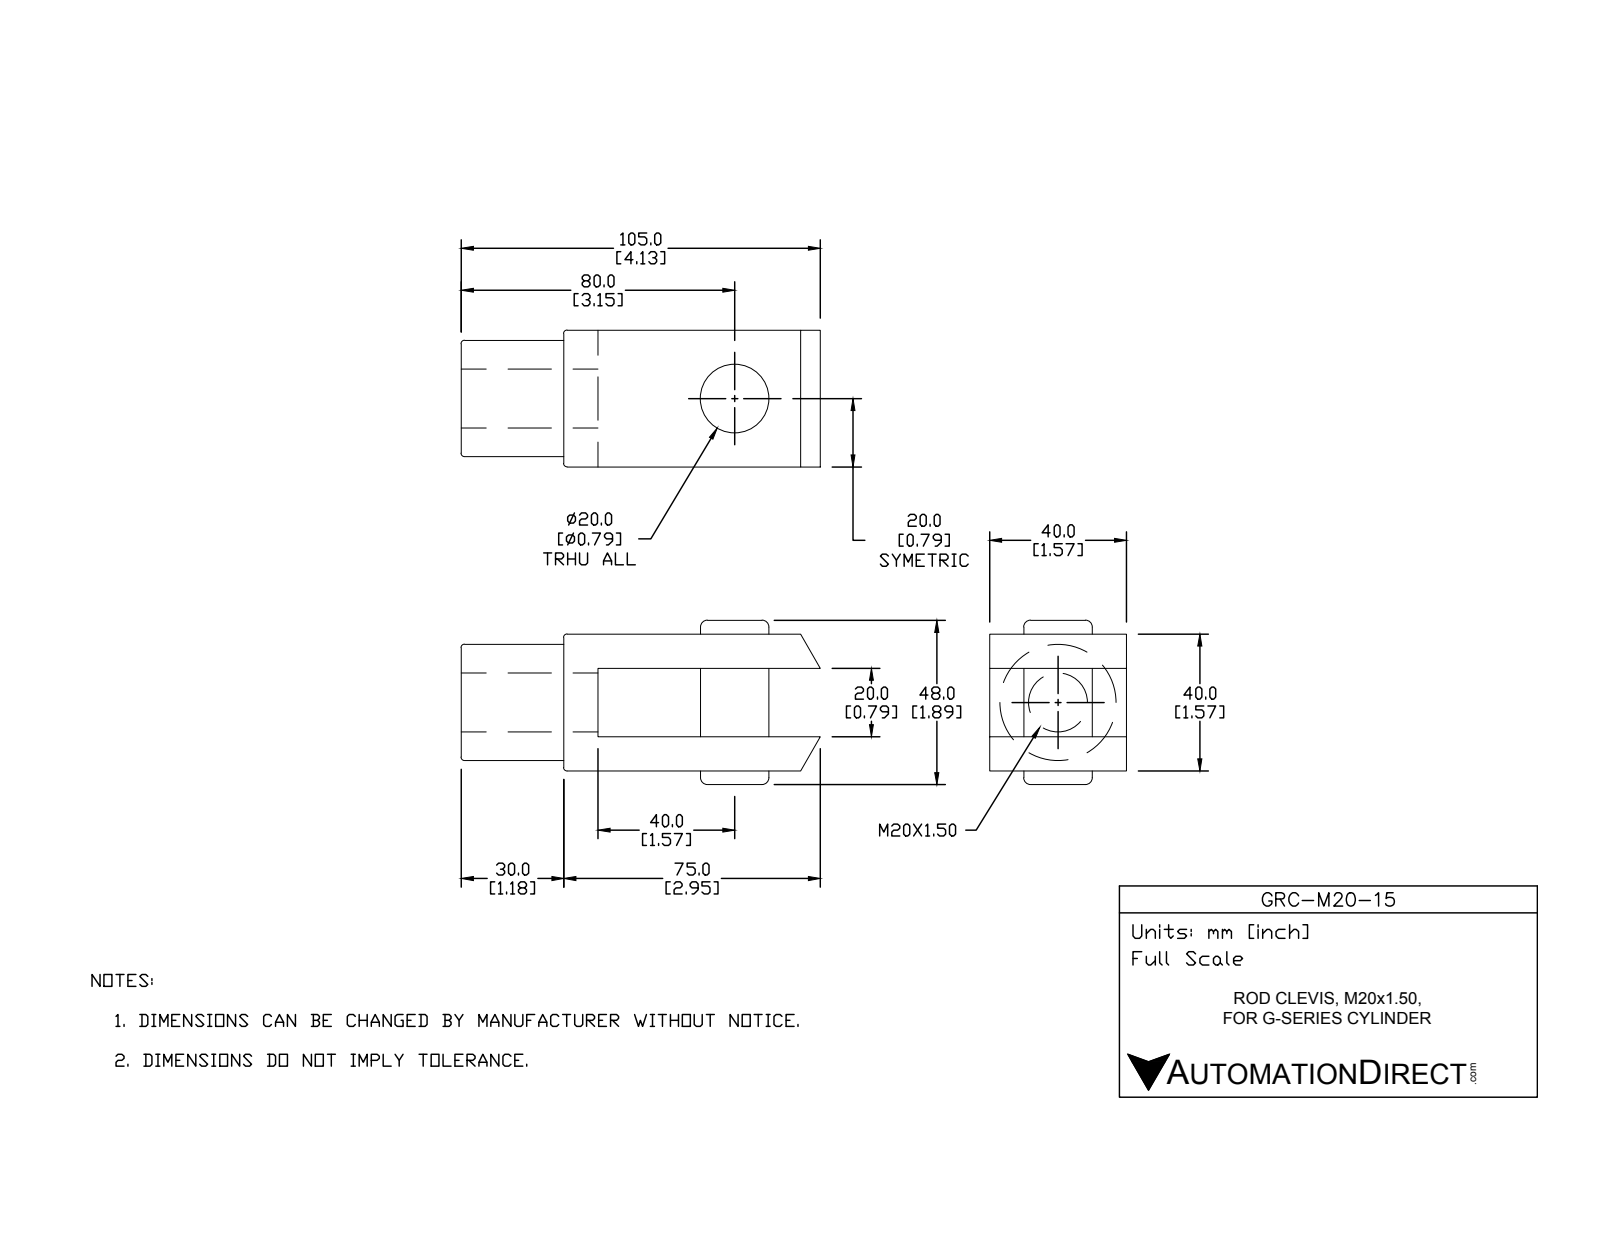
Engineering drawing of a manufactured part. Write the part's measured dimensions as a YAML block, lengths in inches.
part_name: "GRC-M20-15"
step_written_by: "SolidWorks 2017 (AUTOMOTIVE_DESIGN)"
units: inches
bodies: {solids: 1, faces: 33, planar: 13, cylindrical: 14, other: 6}
overall_size: [4.134, 1.89, 1.575]
volume: 5.444
surface_area: 35.81
round_holes:
  - {diameter: 0.728, count: 1}
round_bosses_or_shafts:
  - {diameter: 1.339, count: 1}
  - {diameter: 0.787, count: 1}
partial_cylinders:
  - {radius: 0.039, count: 4}
face_to_face_distances: [1.181, 0.394, 1.575, 0.787, 0.157, 0.551, 1.339, 1.732, 1.89]
